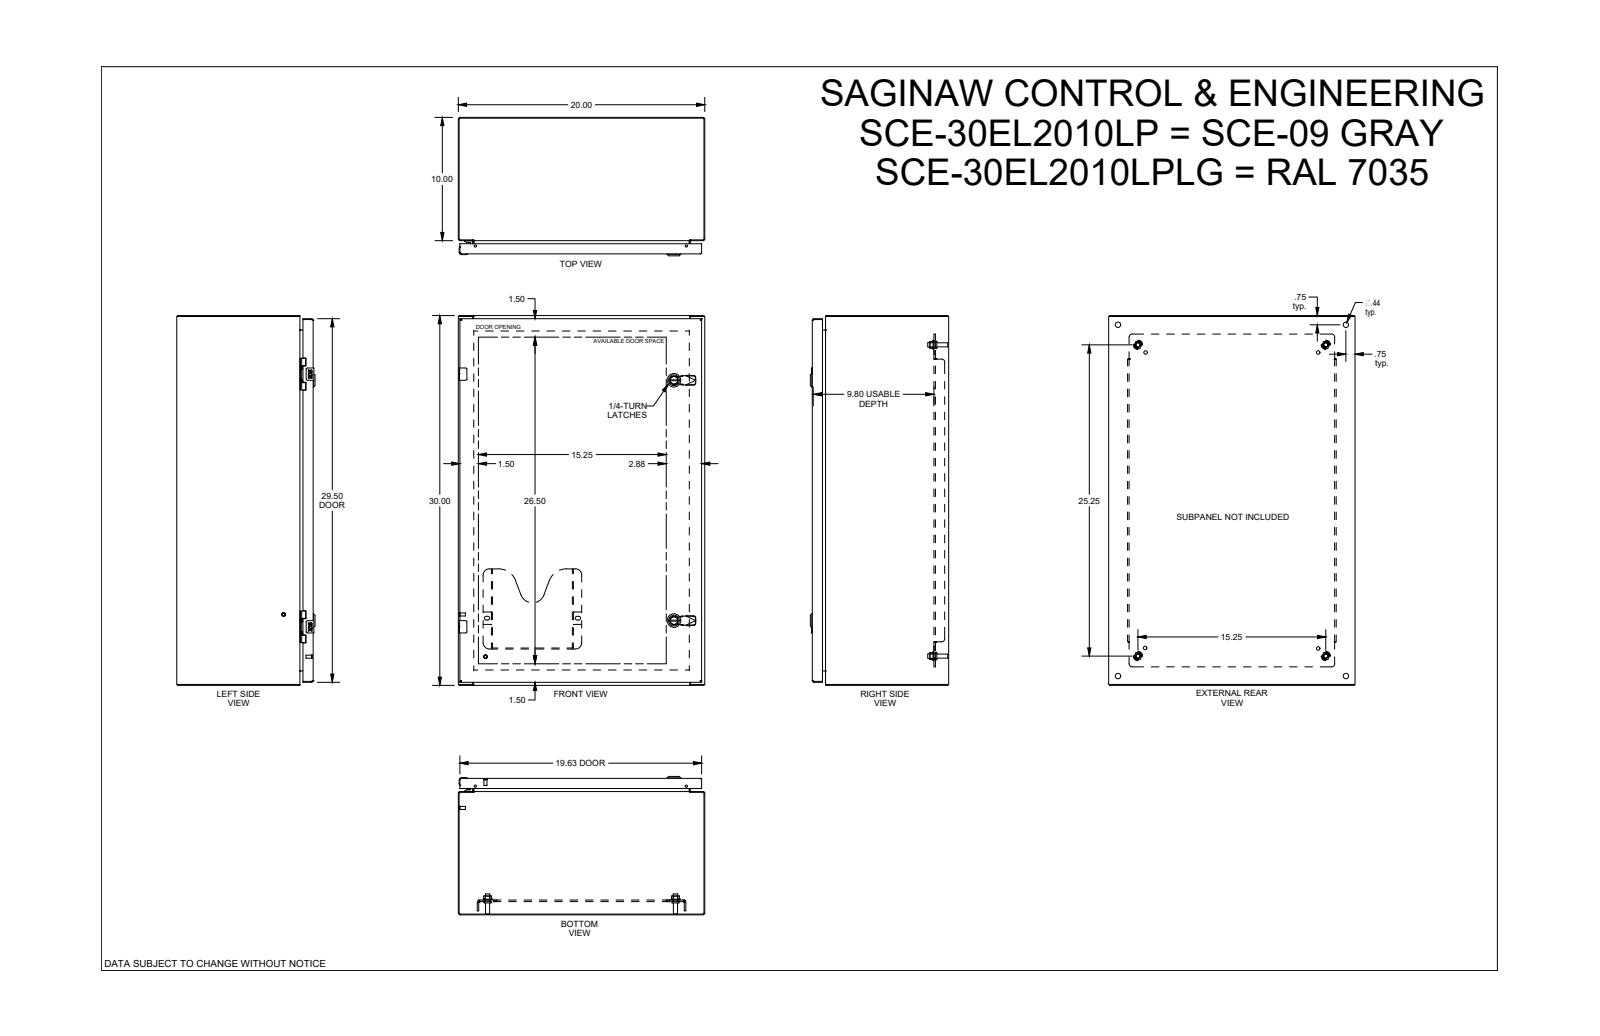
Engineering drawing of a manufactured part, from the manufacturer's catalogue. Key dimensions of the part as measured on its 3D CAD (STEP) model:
Part name (STEP PRODUCT): SCE-30EL2010LP
STEP written by: SolidWorks 2021 (AUTOMOTIVE_DESIGN)
Units: inches
Bodies: 47 solids, 2811 faces (1105 planar, 848 cylindrical, 858 other)
Overall size (bounding box): 30 × 20 × 11.23
Volume: 255.6 in³ · Surface area: 6 196 in²
Round holes (diameter × count): ⌀0.172 ×4, ⌀0.205 ×4, ⌀0.244 ×4, ⌀0.266 ×4, ⌀0.281 ×4, ⌀0.367 ×4, ⌀0.375 ×4, ⌀0.437 ×4, ⌀0.5 ×4, ⌀0.04 ×2, ⌀0.188 ×2, ⌀0.197 ×2
Round bosses / shafts (diameter × count): ⌀0.17 ×6, ⌀0.366 ×4, ⌀0.332 ×4, ⌀0.25 ×4, ⌀0.248 ×4, ⌀0.24 ×4, ⌀0.196 ×3, ⌀1.102 ×2
Partial cylindrical surfaces — rounded edges, fillets, slot ends (radius × count): R0.012 ×56, R0.01 ×28, R0.015 ×24, R0.02 ×20, R0.04 ×17, R0.06 ×13, R0.029 ×12, R0.1 ×12
Main face-to-face distances: 0.075, 0.06, 19.925, 11.073, 10.998, 11.013, 10.938, 1, 0.125, 1.2
Hole centre spacings: 0.985, 20.5, 0.02, 0.493, 0.494, 0.875, 2.298, 4.493
